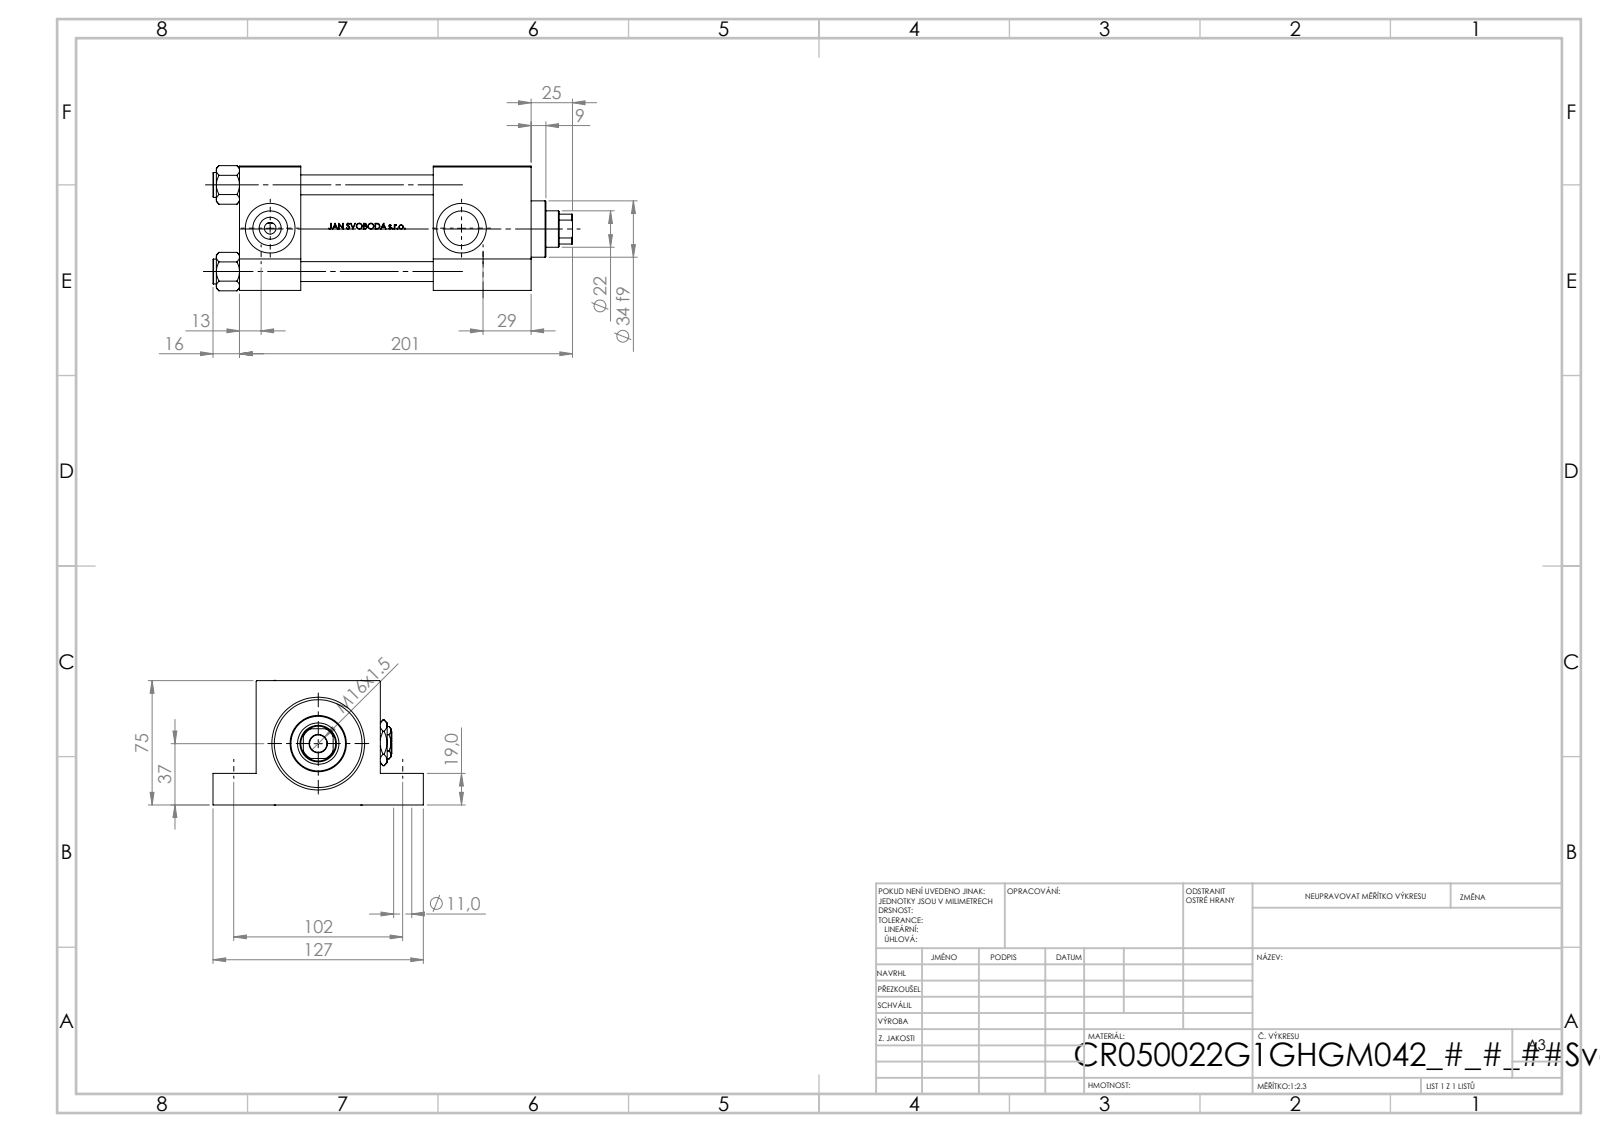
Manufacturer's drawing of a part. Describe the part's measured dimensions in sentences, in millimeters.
The part is named "NUT_M5_G; Zatka_pro_OIL_PORT; V215CR_G_Body; V215_VC_A (+2 more)". Its 3-D file was written by "SolidWorks 2019 (CONFIG_CONTROL_DESIGN)". It is 12 solids with 1134 faces: 454 planar, 128 cylindrical and 552 other. Overall it measures 217 by 127 by 75.54 millimeters. Its volume is 781 708 cubic millimeters and its surface area 173 468 square millimeters. Round holes: 4 of diameter 11, 4 of diameter 12, 2 of diameter 7, 2 of diameter 20.96, 2 of diameter 30, 1 of diameter 10.5, 1 of diameter 22, 1 of diameter 25, 1 of diameter 41, 1 of diameter 50, 1 of diameter 53. Round bosses or shafts: 4 of diameter 15, 1 of diameter 56, 1 of diameter 34. Partial cylindrical surfaces (rounded edges, fillets, slot ends): 1 of radius 10.5. The main face-to-face distances are 75, 37, 176, 139, 101, 19, 56, 117, 80, 59. The hole center spacings are 52.3, 36.63, 37.34, 73.96, 102, 134, 168.4, 115.5.
